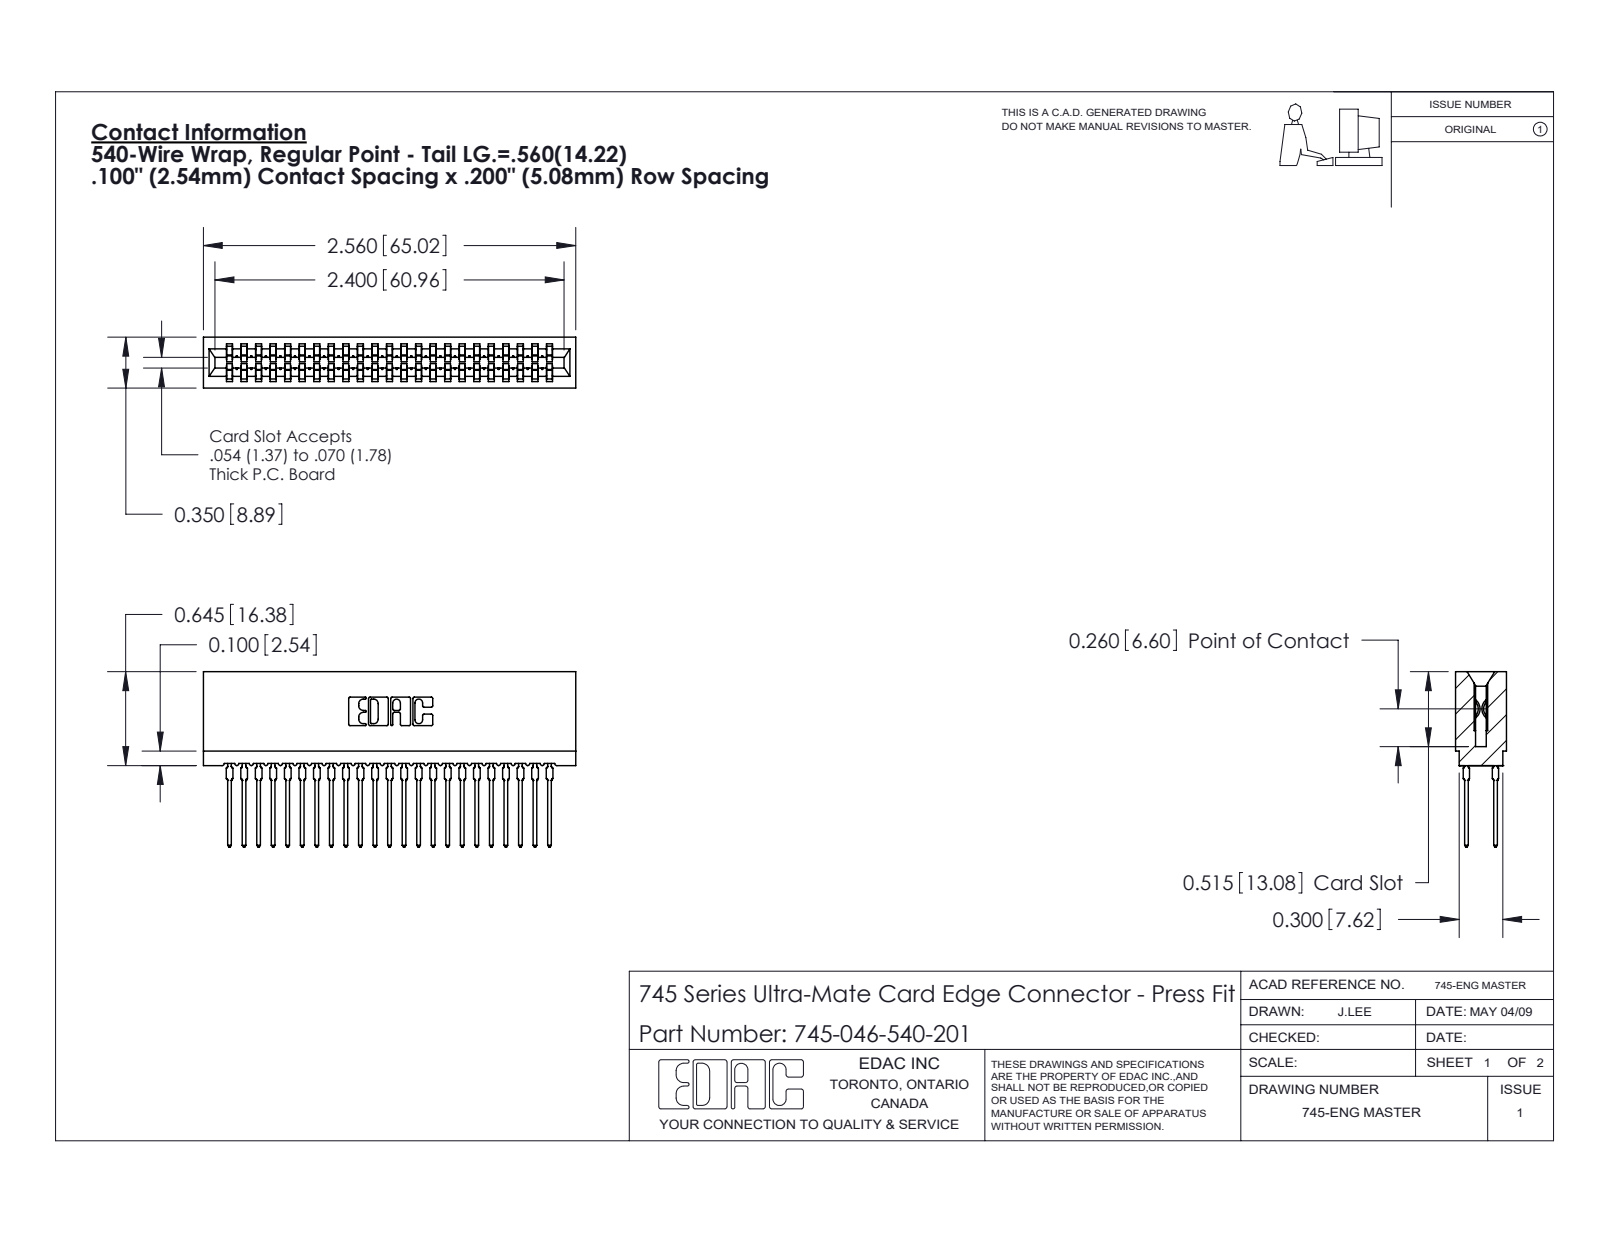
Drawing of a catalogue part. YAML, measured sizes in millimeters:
part_name: "745-046-540-201; 745-292-001_540; 745 Part_Insulator Option - 01"
step_written_by: "SolidWorks 2020 (CONFIG_CONTROL_DESIGN)"
units: millimeters
bodies: {solids: 47, faces: 4212, planar: 2171, cylindrical: 845, other: 1196}
overall_size: [65, 30.6, 8.9]
volume: 6110
surface_area: 12500
partial_cylinders:
  - {radius: 0.5, count: 92}
  - {radius: 0.4, count: 46}
  - {radius: 0.3, count: 22}
  - {radius: 0.1, count: 8}
  - {radius: 0.3, count: 8}
  - {radius: 0.2, count: 6}
  - {radius: 0.8, count: 6}
  - {radius: 0.7, count: 3}
face_to_face_distances: [5.1, 2.5, 1.6, 7.3, 8.9, 7.6, 3.5, 5.4, 1.9, 3.8]
